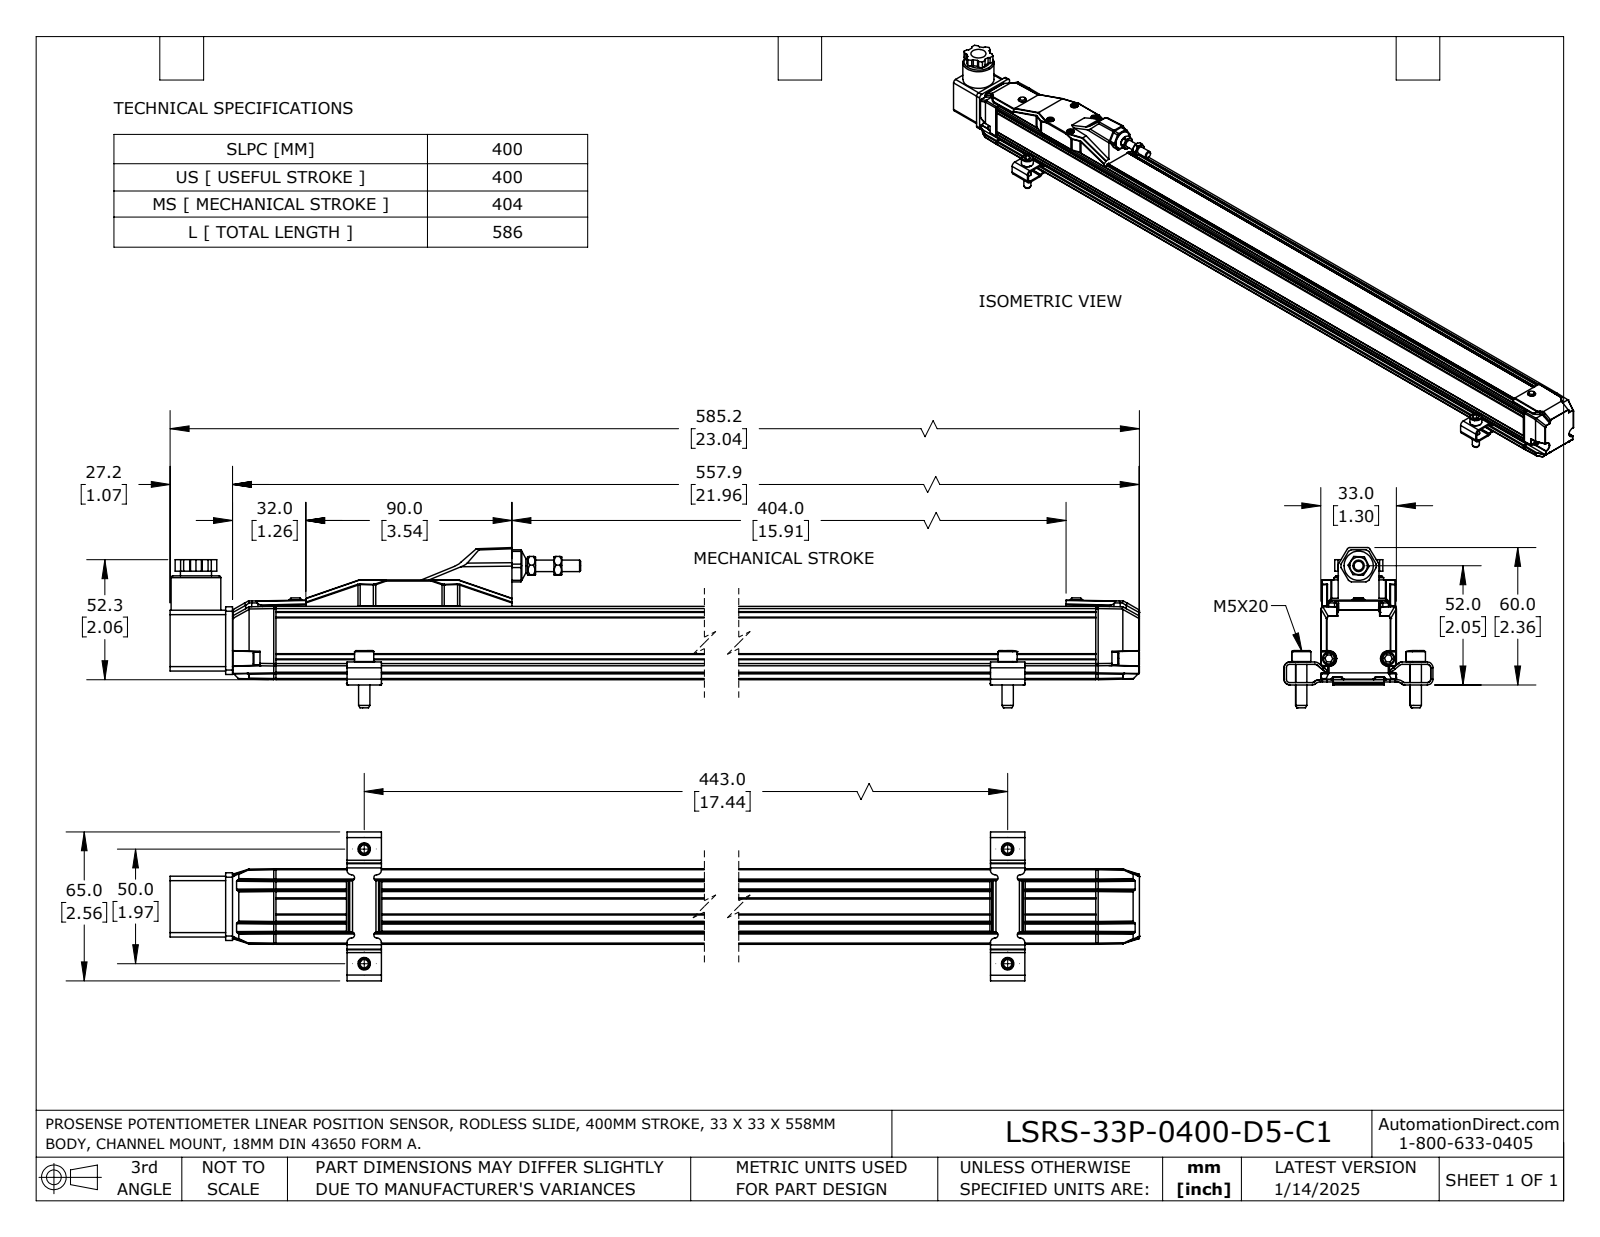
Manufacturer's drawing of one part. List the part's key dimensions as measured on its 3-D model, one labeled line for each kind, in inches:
Part name (STEP PRODUCT): LSRS-33P-0400-D5-C1
STEP written by: SolidWorks 2023 (AUTOMOTIVE_DESIGN)
Units: inches
Bodies: 16 solids, 1348 faces (847 planar, 369 cylindrical, 132 other)
Overall size (bounding box): 23.039 × 2.754 × 2.559
Volume: 34.41 in³ · Surface area: 226 in²
Round holes (diameter × count): ⌀0.106 ×6, ⌀0.185 ×4, ⌀0.217 ×4, ⌀0.13 ×2, ⌀0.11 ×1, ⌀0.157 ×1, ⌀0.197 ×1, ⌀0.209 ×1, ⌀0.232 ×1, ⌀0.236 ×1, ⌀0.276 ×1, ⌀0.394 ×1
Round bosses / shafts (diameter × count): ⌀0.331 ×4, ⌀0.193 ×4, ⌀0.181 ×4, ⌀0.22 ×2, ⌀0.217 ×2, ⌀0.118 ×2, ⌀0.113 ×2, ⌀0.113 ×2
Partial cylindrical surfaces — rounded edges, fillets, slot ends (radius × count): R0.02 ×82, R0.008 ×62, R0.079 ×44, R0.118 ×26, R0.039 ×10, R0.051 ×8, R0.059 ×8, R0.157 ×8
Main face-to-face distances: 1.299, 1.244, 0.118, 1.167, 0.237, 1.007, 0.035, 0.014, 1.285, 0.443
Hole centre spacings: 0.597, 0.787, 0.933, 1.221, 1.286, 1.673, 1.969, 16.288
